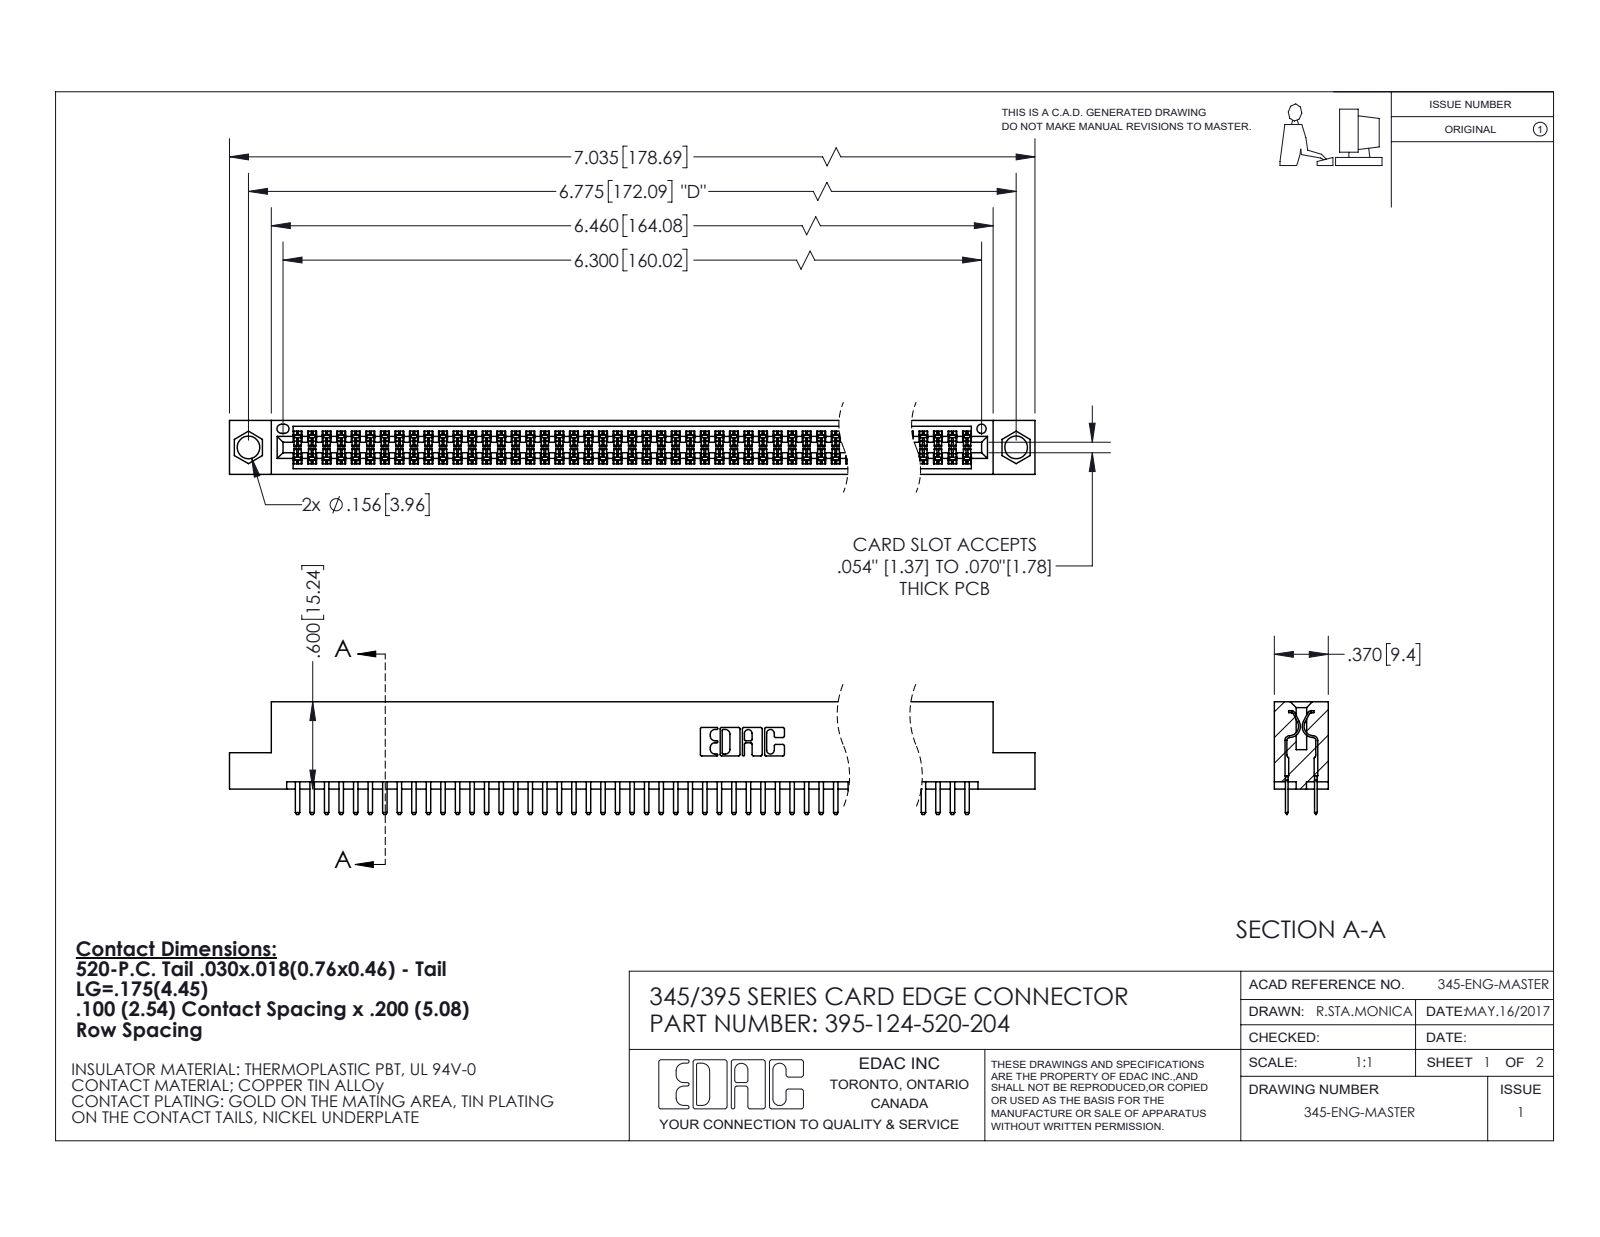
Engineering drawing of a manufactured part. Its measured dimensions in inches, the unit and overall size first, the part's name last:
Units: inches
Overall size (bounding box): 7.035 × 0.775 × 0.37
Round holes (diameter × count): ⌀0.156 ×2, ⌀0.064 ×1
Partial cylindrical surfaces — rounded edges, fillets, slot ends (radius × count): R0.006 ×186, R0.01 ×128, R0.01 ×22, R0.007 ×6, R0.031 ×6, R0.026 ×3, R0.014 ×2, R0.019 ×2
Main face-to-face distances: 0.298, 0.072, 0.2, 0.37, 0.098, 0.272, 0.025, 0.225, 0.022, 0.072
Hole centre spacings: 0.27, 6.539, 6.775
Volume: 1.061 in³ · Surface area: 40.02 in²
Bodies: 125 solids, 6836 faces (4434 planar, 2402 cylindrical, 0 other)
Part name (STEP PRODUCT): 345-292-001_345-293-120; 345 Part_Flush Mounting Lugs - 0.156 Dia-TI; 395-124-520-204
STEP written by: SolidWorks 2020 (CONFIG_CONTROL_DESIGN)
